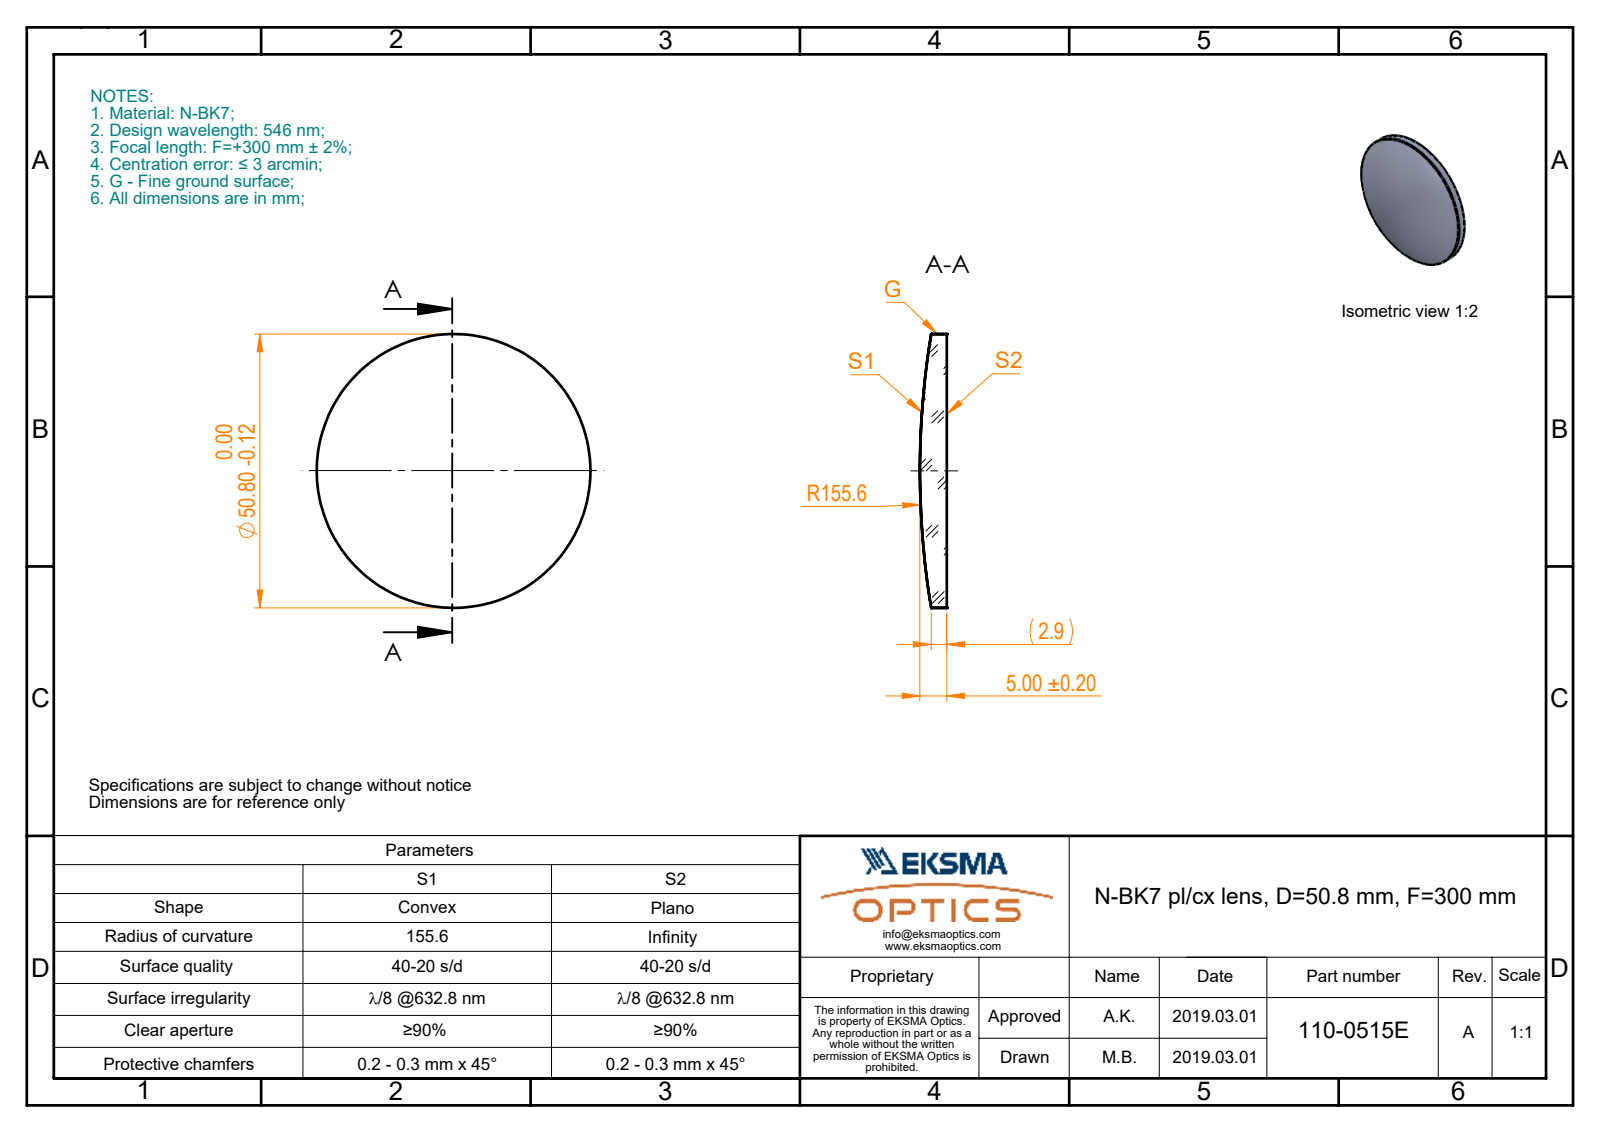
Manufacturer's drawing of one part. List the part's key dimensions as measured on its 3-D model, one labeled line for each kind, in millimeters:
Part name (STEP PRODUCT): 110-0515E BK7 pl-cx 50.8 F300
STEP written by: SolidWorks 2017 (CONFIG_CONTROL_DESIGN)
Units: millimetres
Bodies: 1 solid, 5 faces (1 planar, 2 cylindrical, 2 other)
Overall size (bounding box): 50.8 × 50.8 × 5
Volume: 8 024 mm³ · Surface area: 4 532 mm²
Round bosses / shafts (diameter × count): ⌀50.8 ×1
